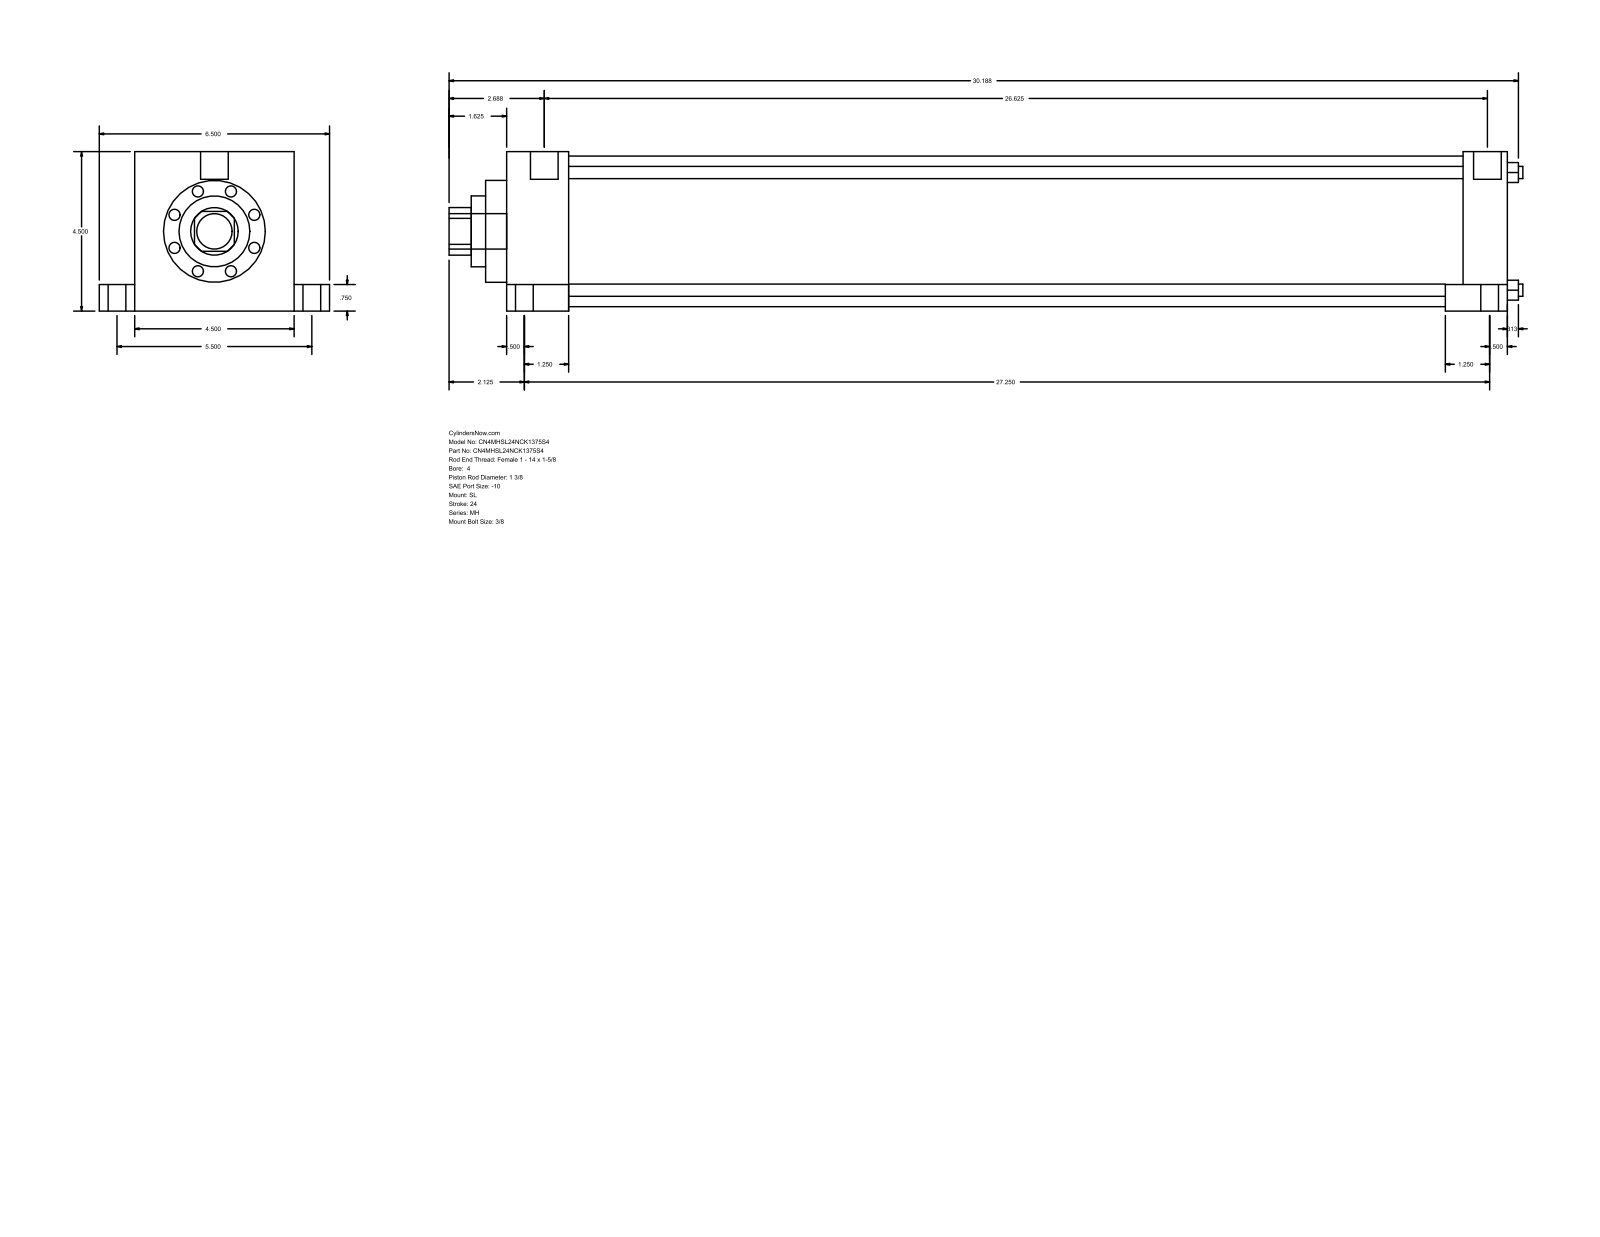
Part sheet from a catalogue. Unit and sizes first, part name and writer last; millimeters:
Units: millimetres
Overall size (bounding box): 769.94 × 165.1 × 114.3
Round holes (diameter × count): ⌀8.76 ×4, ⌀34.92 ×1, ⌀50.8 ×1, ⌀73.03 ×1, ⌀107.95 ×1
Round bosses / shafts (diameter × count): ⌀19.05 ×4, ⌀12.7 ×4, ⌀8.73 ×4, ⌀19.84 ×2, ⌀25.4 ×1
Partial cylindrical surfaces — rounded edges, fillets, slot ends (radius × count): R17.06 ×1
Main face-to-face distances: 114.3, 717.56, 44.45, 673.11, 685.81, 641.36, 31.75, 25.4, 139.7, 19.05
Hole centre spacings: 59.62, 84.32, 119.25
Bodies: 0 solids, 110 faces (77 planar, 33 cylindrical, 0 other)
Part name (STEP PRODUCT): MH_SL__0400_1.375
STEP written by: GSSL Pune (CONFIG_CONTROL_DESIGN)
